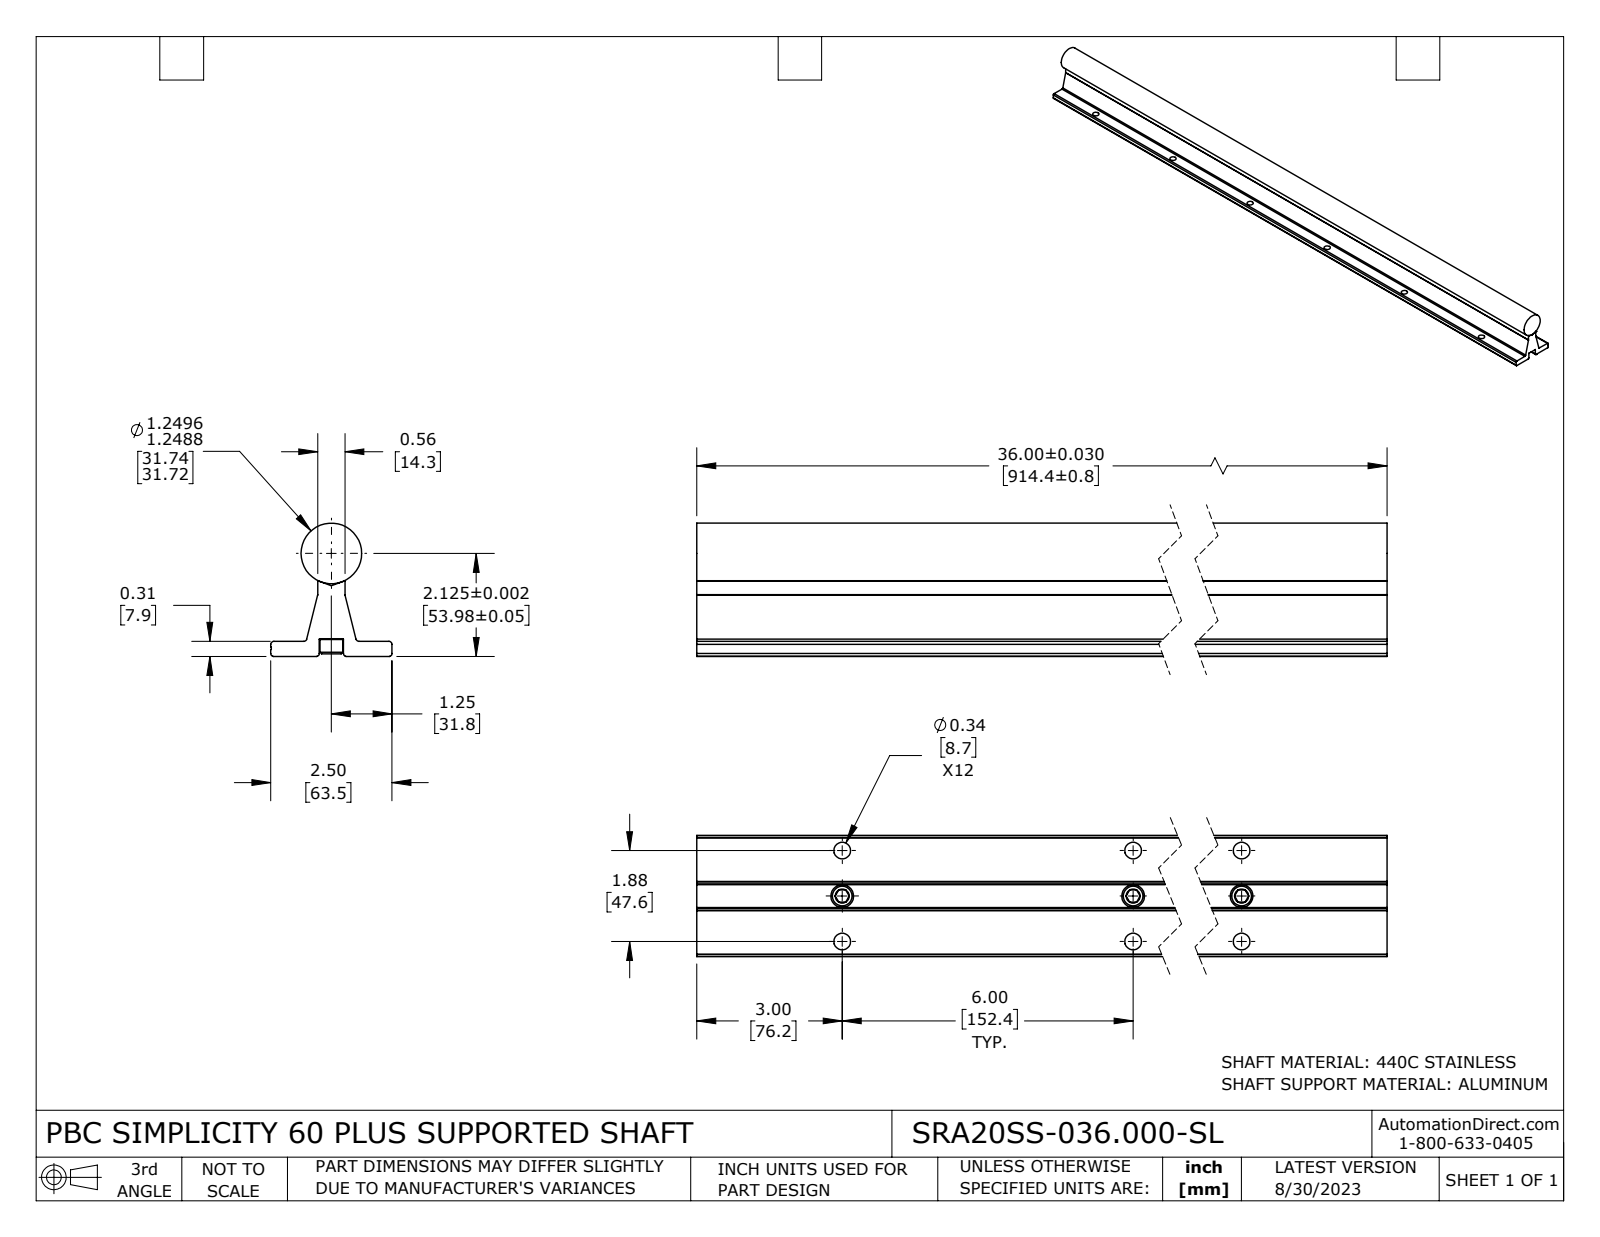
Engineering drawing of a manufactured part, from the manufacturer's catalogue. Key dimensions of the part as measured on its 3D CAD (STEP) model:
Part name (STEP PRODUCT): SRA20SS-036.000-SL
STEP written by: SolidWorks 2021 (CONFIG_CONTROL_DESIGN)
Units: inches
Bodies: 8 solids, 283 faces (93 planar, 100 cylindrical, 90 other)
Overall size (bounding box): 36 × 2.75 × 2.5
Volume: 97.74 in³ · Surface area: 473.7 in²
Round holes (diameter × count): ⌀0.344 ×18, ⌀0.272 ×6, ⌀0.375 ×6
Round bosses / shafts (diameter × count): ⌀0.469 ×6, ⌀0.313 ×6, ⌀1.25 ×1
Partial cylindrical surfaces — rounded edges, fillets, slot ends (radius × count): R0.063 ×6, R0.062 ×3, R0.015 ×2, R0.033 ×2, R0.063 ×1
Main face-to-face distances: 0.313, 0.031, 0.531, 0.367, 0.055, 0.969, 1, 1.5, 1.531, 0.5
Hole centre spacings: 6.073, 12.037, 6, 0.937, 12, 18.024, 6.286, 18
